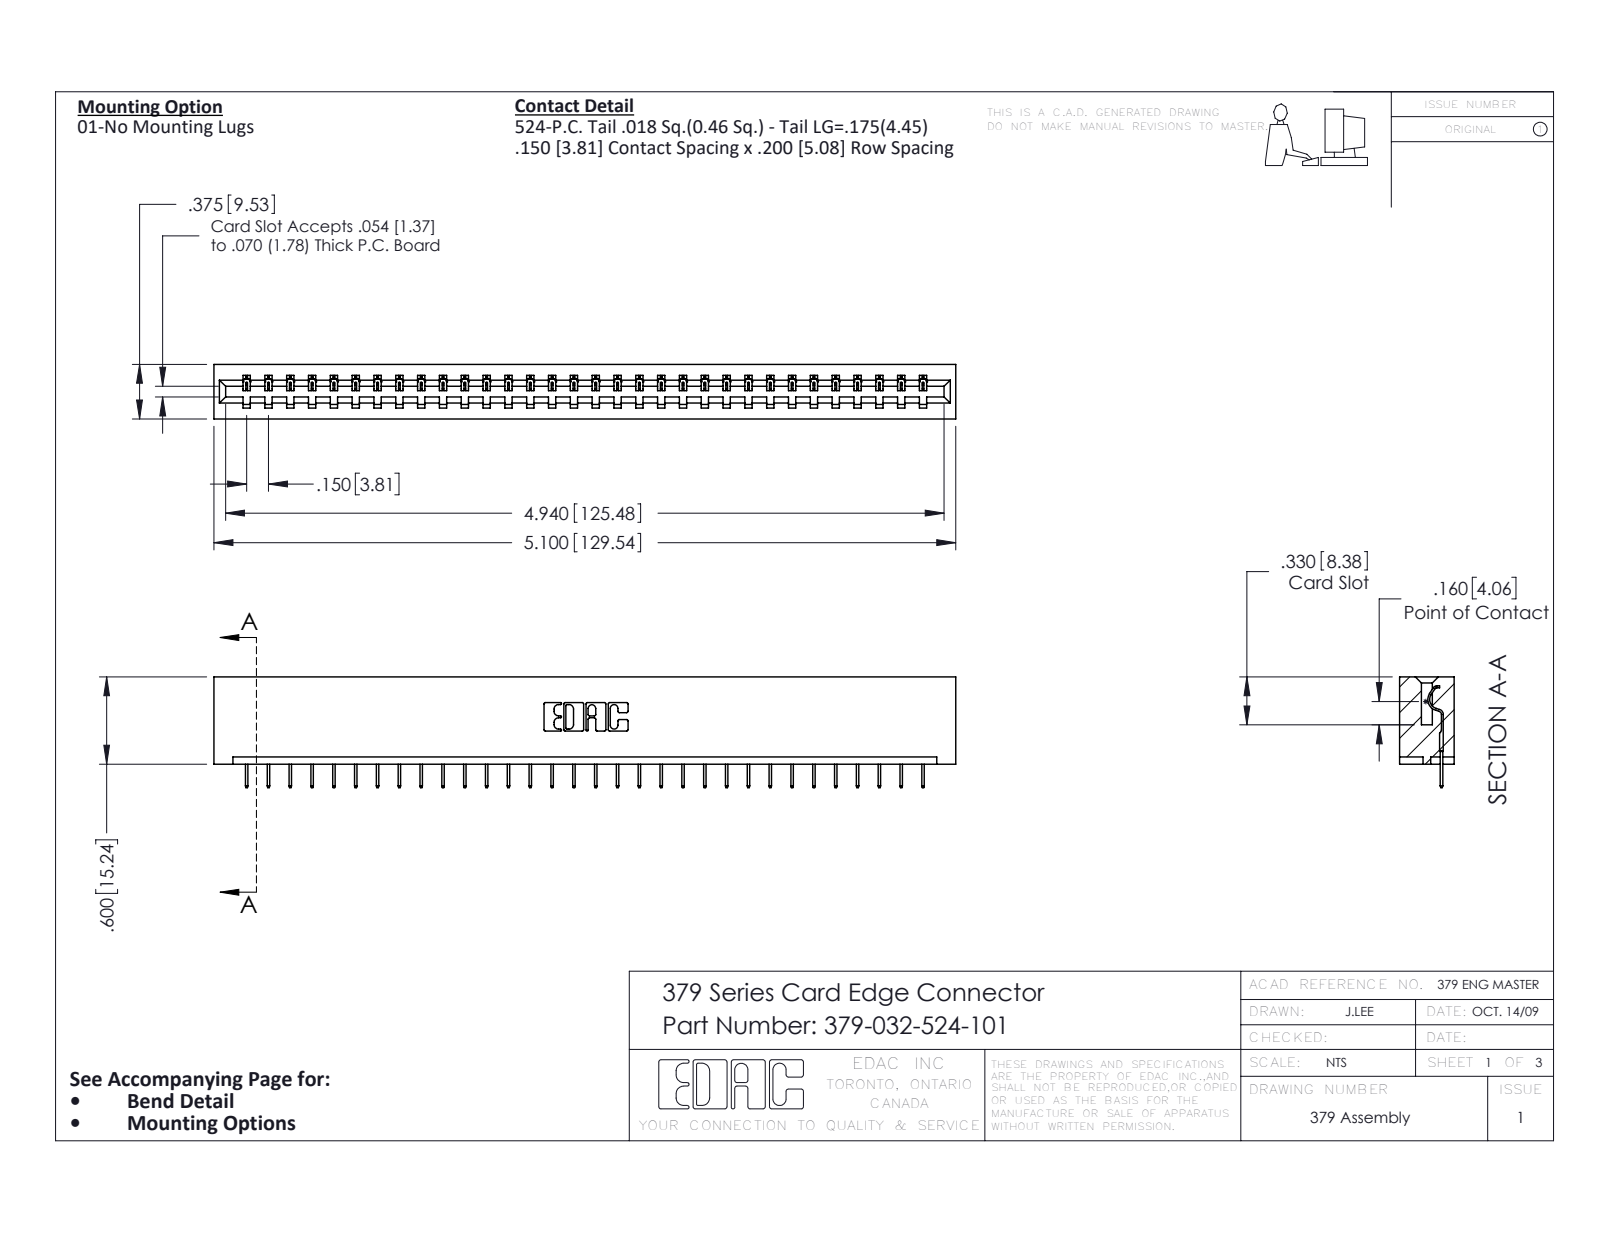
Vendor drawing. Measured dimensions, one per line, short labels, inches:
name: 345-292-001_345-293-124; 379 Part_Lugless; 379-032-524-101
written by: SolidWorks 2016 (CONFIG_CONTROL_DESIGN)
unit: in
bodies: 33 solids, 2090 faces (1602 planar, 488 cylindrical, 0 other)
size: 5.1 × 0.762 × 0.375
volume: 0.859 in³; area: 21.51 in²
rounds: 64× R0.006, 22× R0.01, 6× R0.007, 6× R0.031, 3× R0.026, 1× R0.014, 1× R0.022, 1× R0.024
face distances: 0.3, 0.075, 0.375, 0.225, 0.6, 0.15, 0.55, 0.45, 0.15, 0.15
